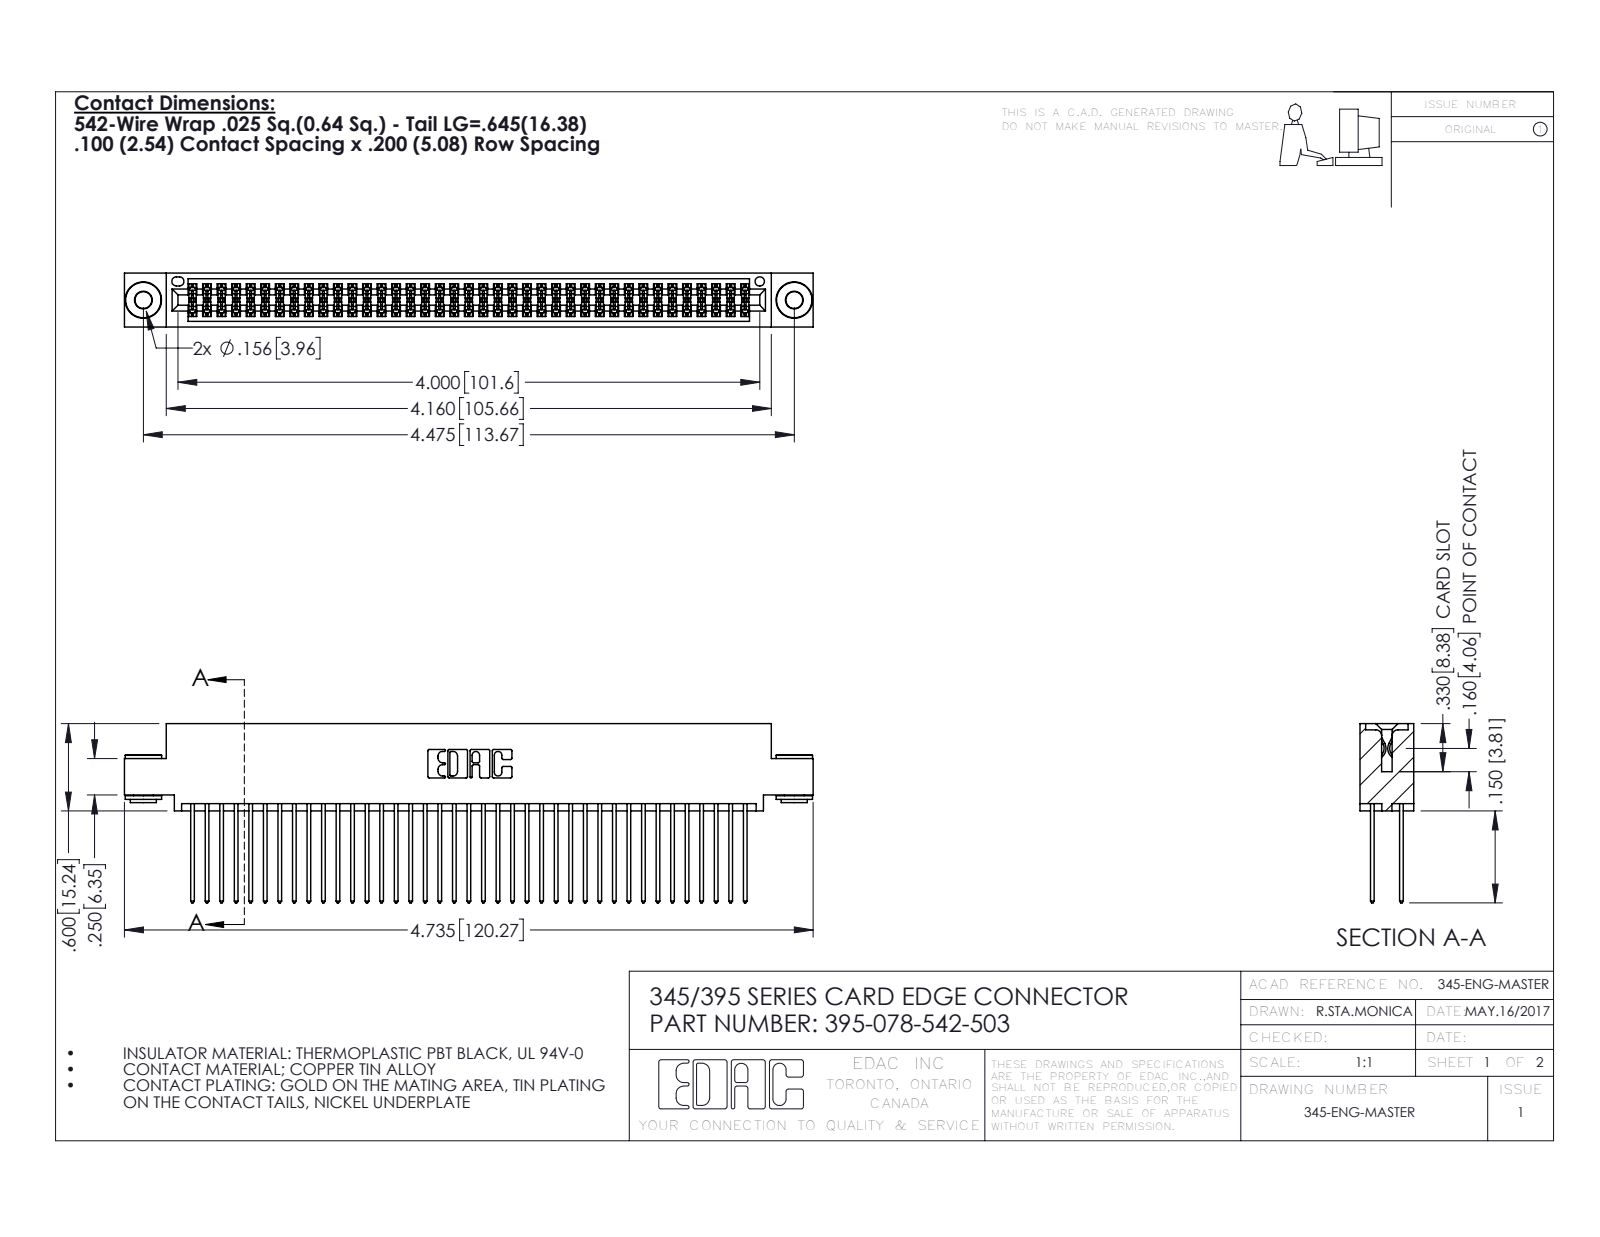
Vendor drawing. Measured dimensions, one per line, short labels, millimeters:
name: 395-078-542-503; 345-292-001_345-293-142; 345-250-002_345-250-002-102; 345 Part_0.110 Offset - 0.156 Dia-TH
written by: SolidWorks 2016 (CONFIG_CONTROL_DESIGN)
unit: mm
bodies: 81 solids, 4068 faces (2668 planar, 1392 cylindrical, 8 other)
size: 120.3 × 31.3 × 9.4
volume: 12 000 mm³; area: 19 630 mm²
holes: 2× ⌀2.9, 2× ⌀4, 1× ⌀1.6
bosses: 2× ⌀6.4, 2× ⌀4.6, 2× ⌀3.5
rounds: 117× R0.2, 78× R0.3, 22× R0.3, 6× R0.2, 6× R0.8, 3× R0.7, 2× R0.4, 2× R0.5
face distances: 1.8, 7.6, 5.1, 0.6, 2.5, 6.9, 5.7, 9.4, 4.4, 3.8
hole spacings: 6.9, 107.7, 113.7
